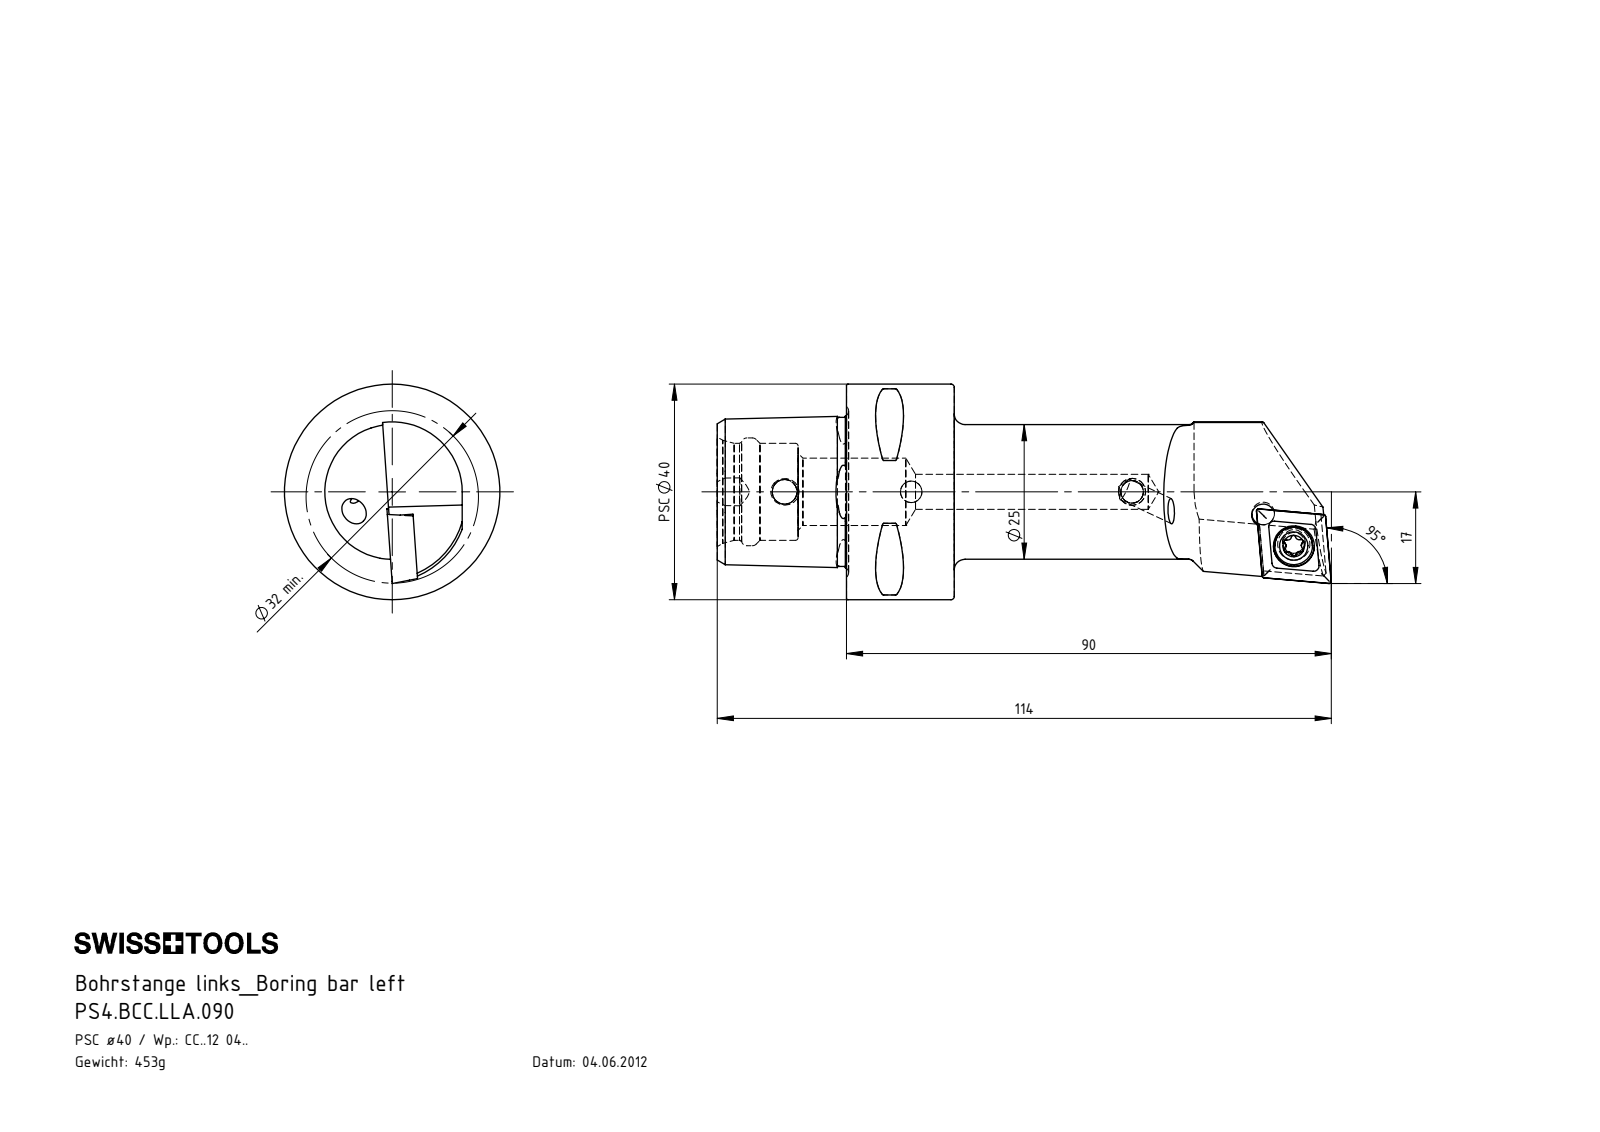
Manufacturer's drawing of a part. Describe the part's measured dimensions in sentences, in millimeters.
The part is named "PS4-BCC.LLA.090_A; PS4.BCC.LLA.090; KVT_MB_600_050; CCMT120404 (+1 more)". Its 3-D file was written by "SolidWorks 2017 (AUTOMOTIVE_DESIGN)". It is 5 solids with 289 faces: 49 planar, 75 cylindrical and 165 other. Overall it measures 114 by 40 by 40 millimeters. Its volume is 57 707 cubic millimeters and its surface area 15 991 square millimeters. Round holes: 4 of diameter 4.2, 2 of diameter 4, 1 of diameter 4.6, 1 of diameter 5.5, 1 of diameter 6.5, 1 of diameter 7.6, 1 of diameter 12.5, 1 of diameter 18, 1 of diameter 20. Round bosses or shafts: 2 of diameter 5, 1 of diameter 40, 1 of diameter 25, 1 of diameter 7. Partial cylindrical surfaces (rounded edges, fillets, slot ends): 8 of radius 0.3, 6 of radius 0.39, 3 of radius 0.69, 3 of radius 0.69, 2 of radius 3, 1 of radius 13, 1 of radius 15. The main face-to-face distances are 20, 4.46, 24, 44, 15.52, 35.3, 15, 9, 29, 4.76. The hole center spacings are 8.04, 8.09, 23.5, 41, 64.5.
